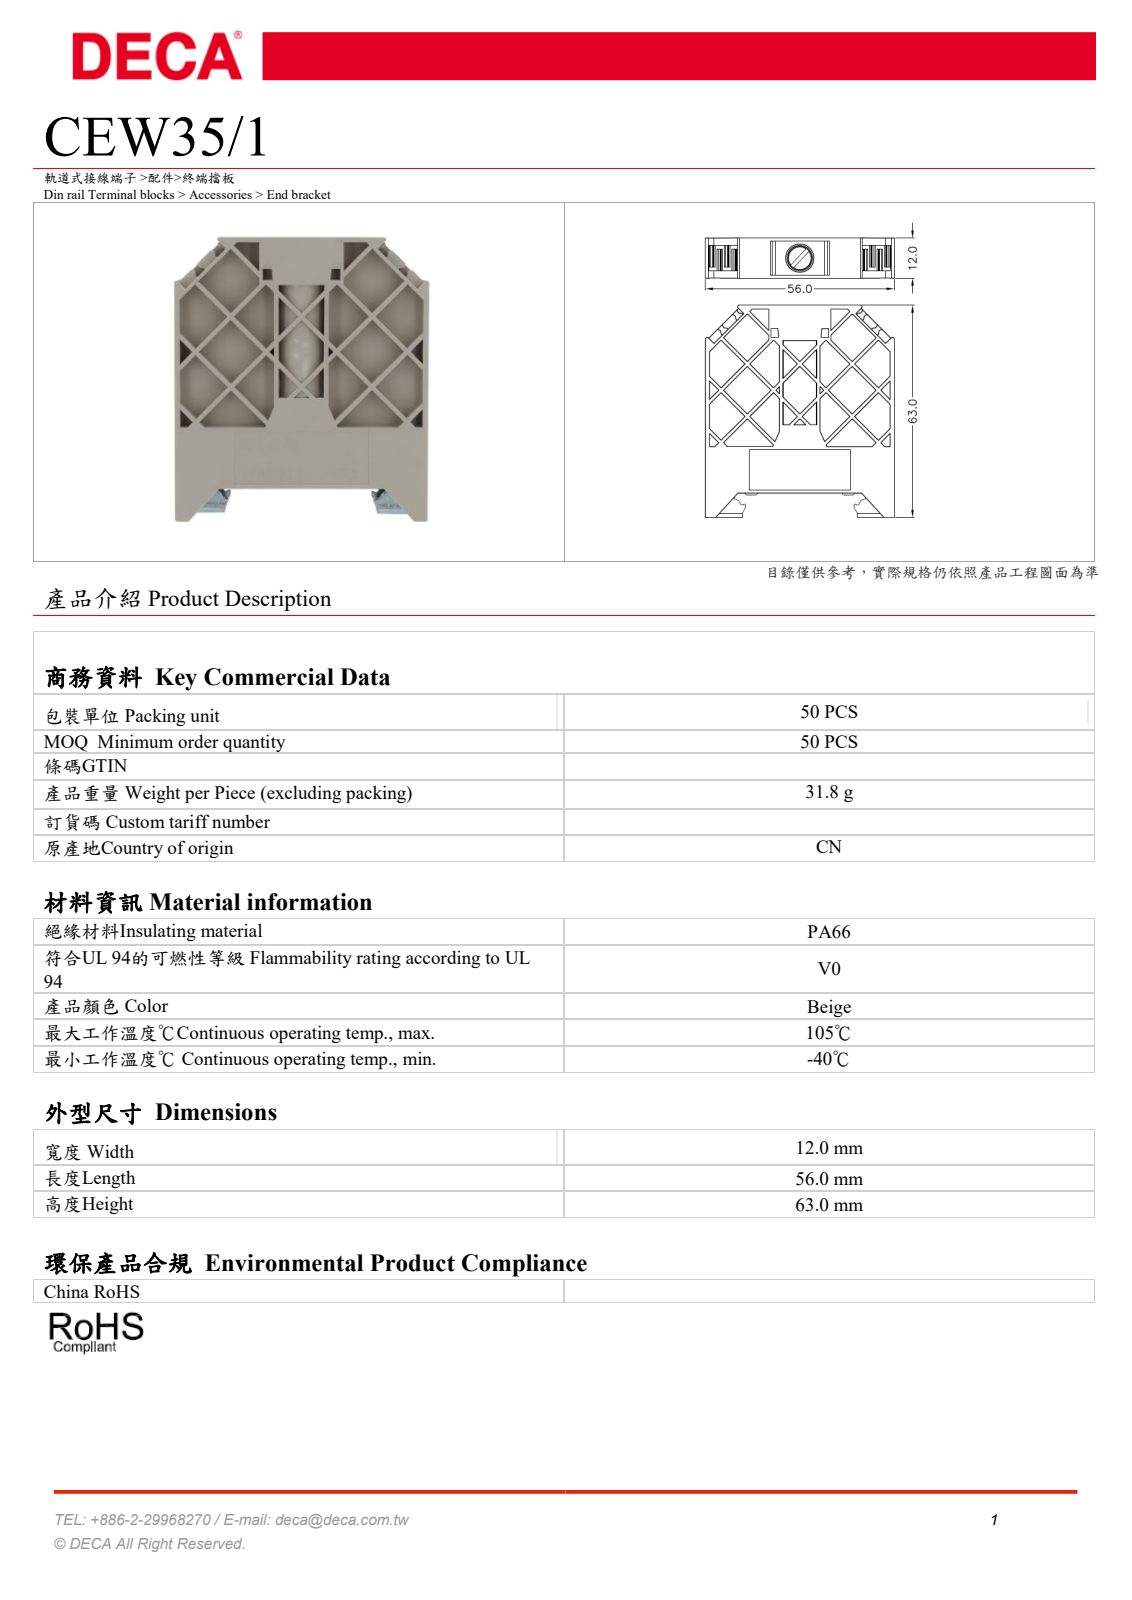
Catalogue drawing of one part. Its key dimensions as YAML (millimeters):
part_name: "CEW351"
step_written_by: "XStep 1.0 (CONFIG_CONTROL_DESIGN) ( ))"
units: millimeters
bodies: {solids: 1, faces: 55, planar: 38, cylindrical: 17, other: 0}
overall_size: [1600.2, 1422.4, 304.8]
volume: 590100000
surface_area: 6327000
round_holes:
  - {diameter: 212.54, count: 1}
partial_cylinders:
  - {radius: 12.7, count: 10}
  - {radius: 5.08, count: 2}
  - {radius: 25.4, count: 2}
  - {radius: 50.8, count: 2}
face_to_face_distances: [304.8, 1422.4, 25.4, 279.4, 1414.78, 139.67, 1554.45, 254, 502.92, 919.48]
